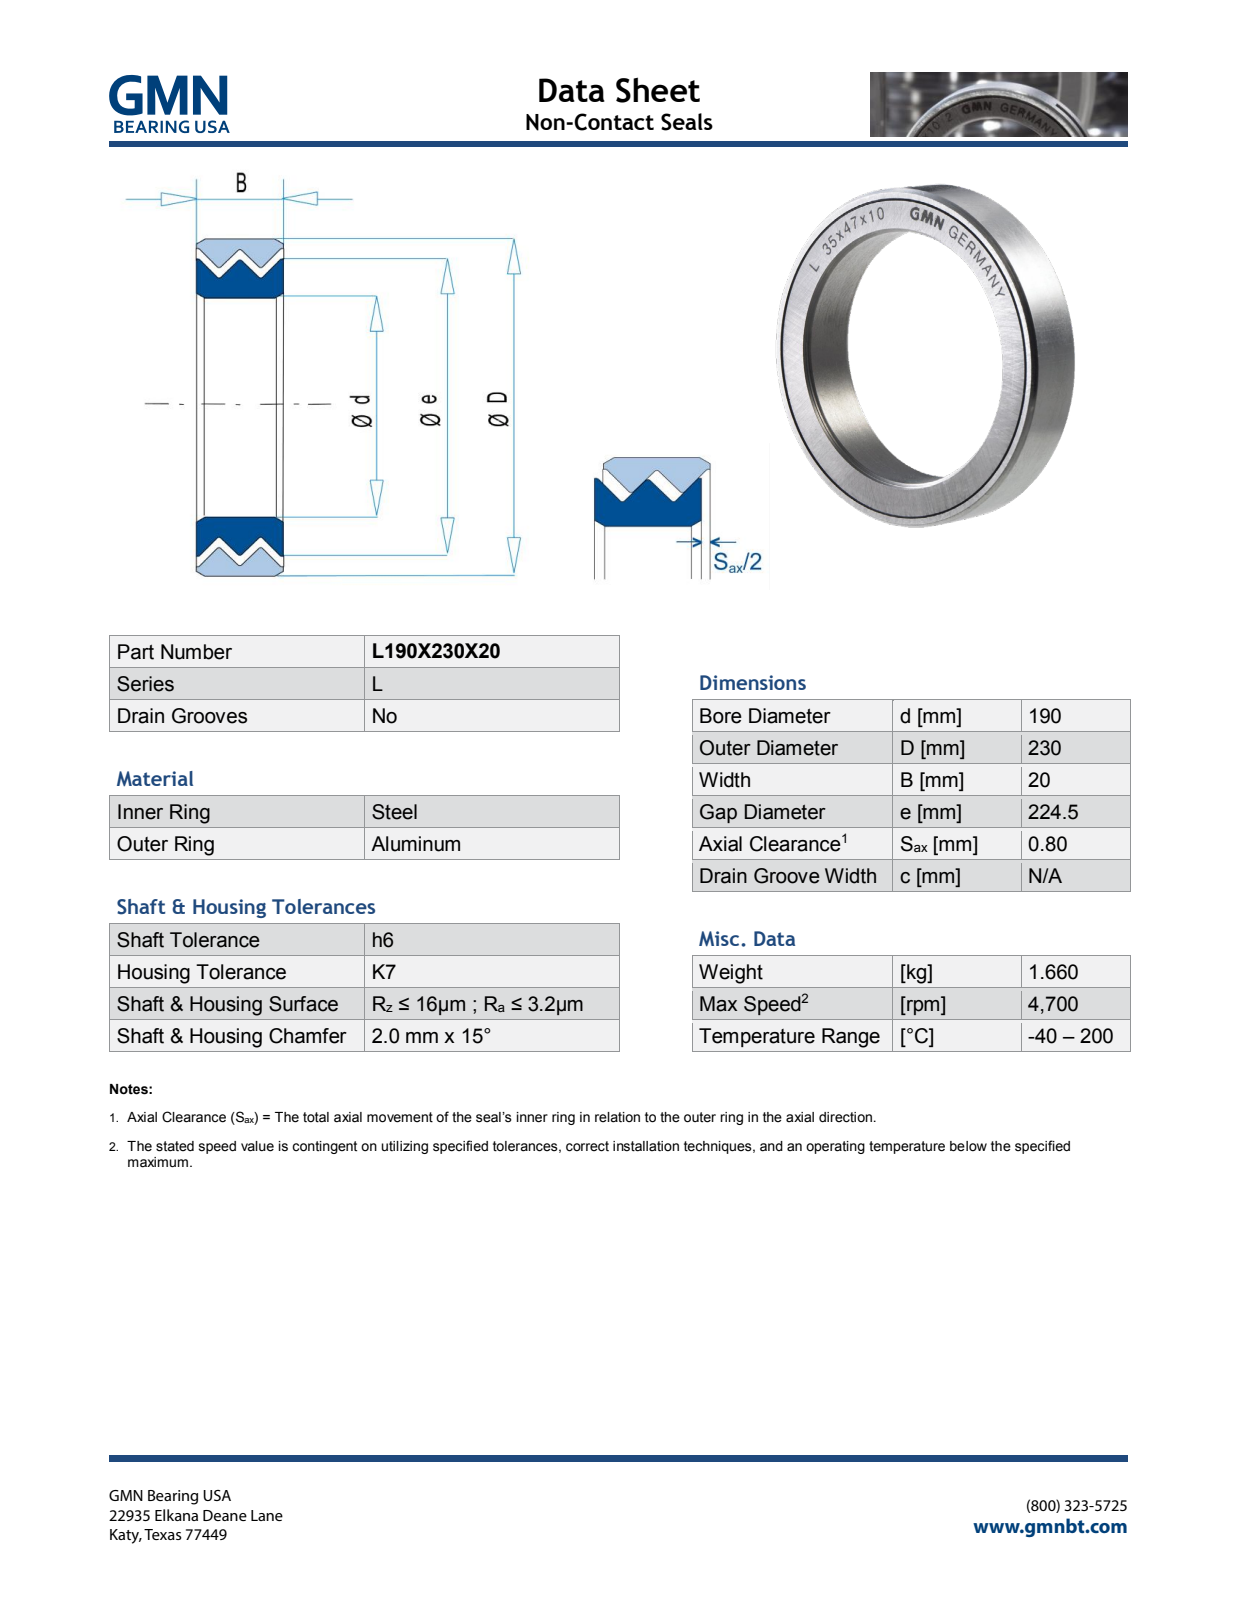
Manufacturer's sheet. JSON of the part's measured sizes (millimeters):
{"part_name": "L190X230X20_PRT", "step_written_by": "PRO/ENGINEER BY PARAMETRIC TECHNOLOGY CORPORATION, 2013150 (AUTOMOTIVE_DESIGN)", "units": "millimeters", "bodies": {"solids": 1, "faces": 713, "planar": 633, "cylindrical": 8, "other": 72}, "overall_size": [230, 230, 20.08], "volume_mm3": 255486, "surface_area_mm2": 86843, "round_holes": [[190, 1], [223.91, 1]], "round_bosses_or_shafts": [[230, 1]], "face_to_face_distances": [20, 20.08, 1.76, 14.1, 12.34, 1.77, 1.8, 9.98, 11.74, 14.09]}
